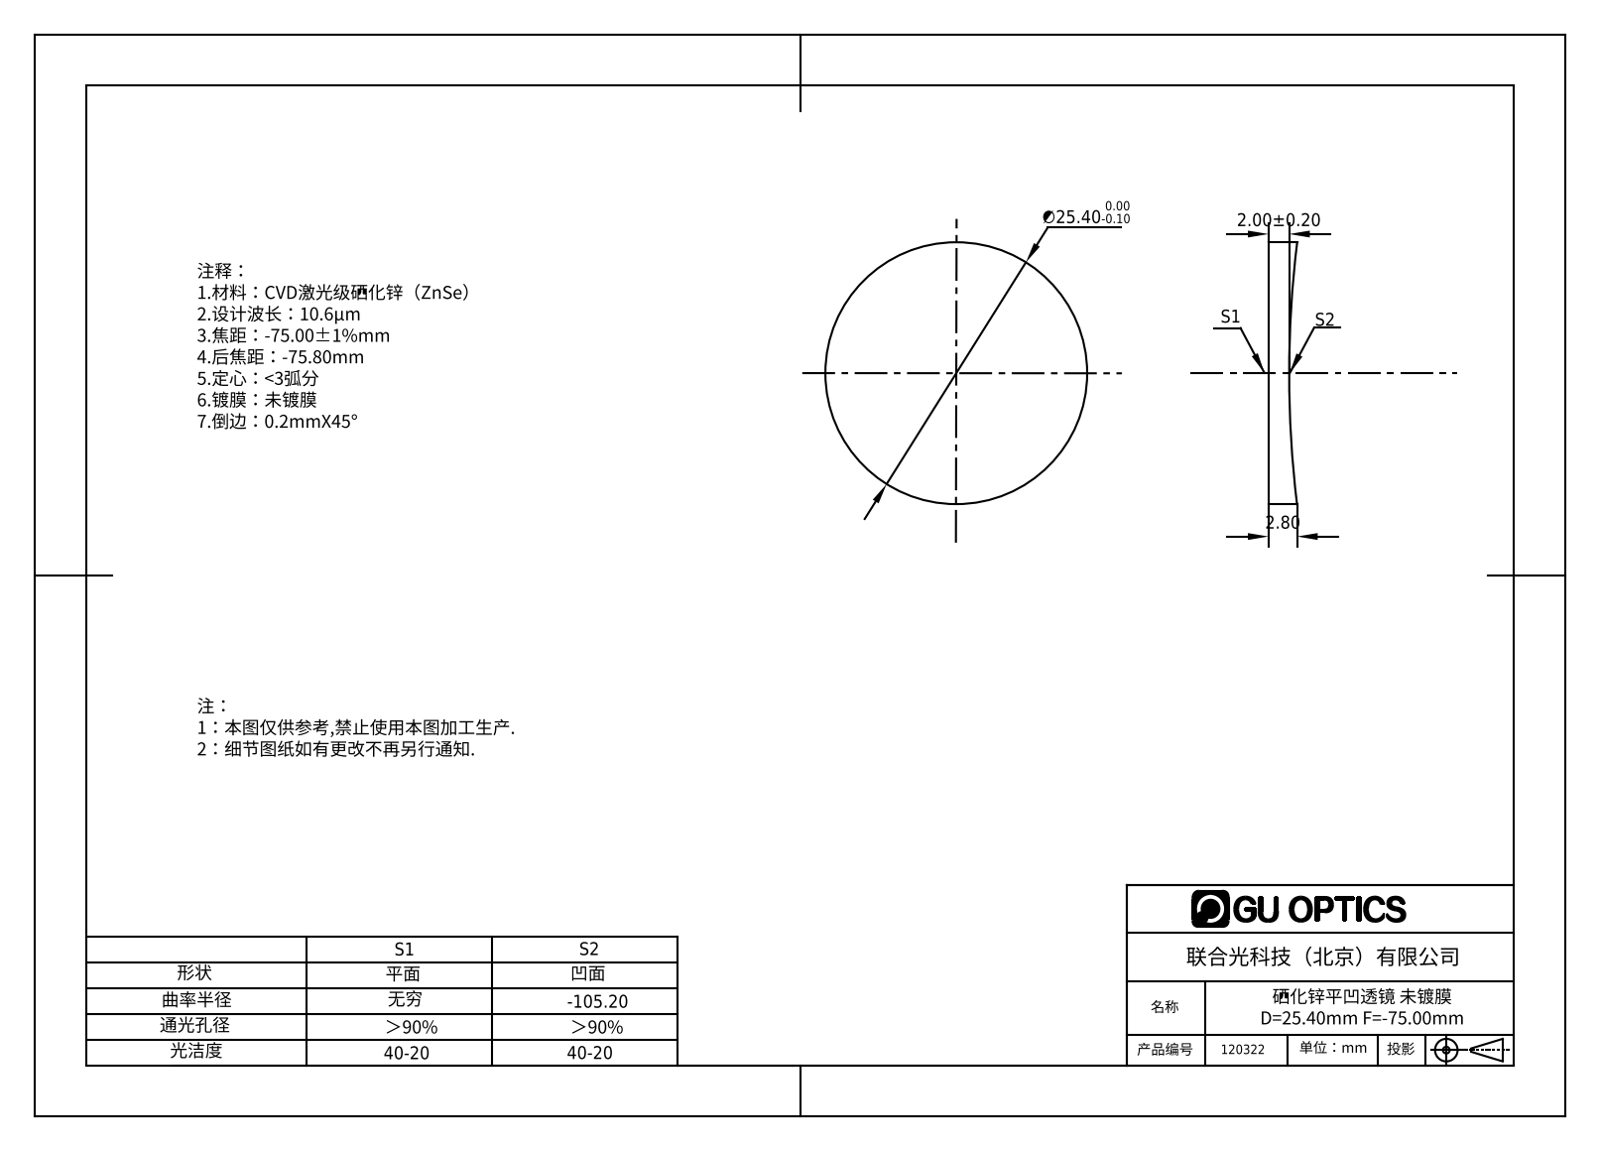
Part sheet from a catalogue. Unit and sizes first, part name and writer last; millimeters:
Units: millimetres
Overall size (bounding box): 25.4 × 25.4 × 2.77
Round bosses / shafts (diameter × count): ⌀25.4 ×1
Volume: 1 210 mm³ · Surface area: 1 237 mm²
Bodies: 1 solid, 5 faces (1 planar, 2 cylindrical, 2 other)
Part name (STEP PRODUCT): 120322
STEP written by: SolidWorks 2016 (AUTOMOTIVE_DESIGN)
